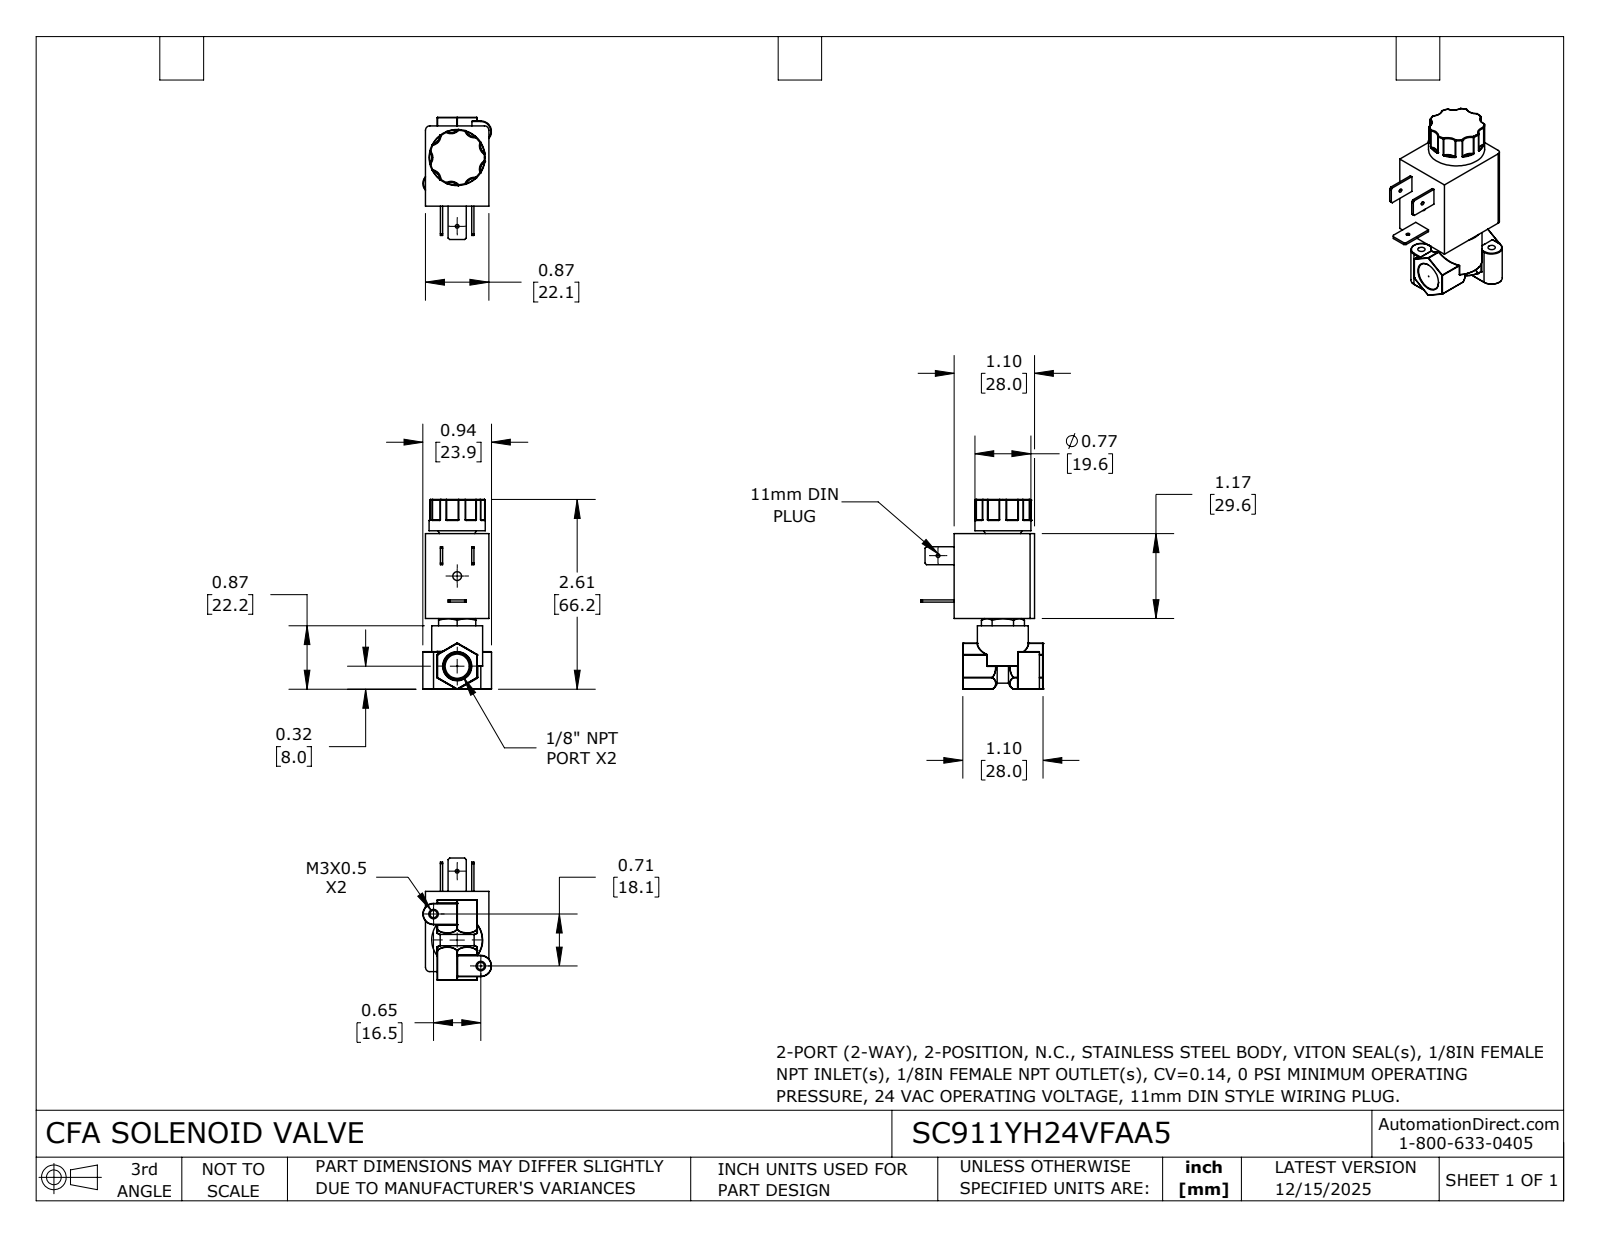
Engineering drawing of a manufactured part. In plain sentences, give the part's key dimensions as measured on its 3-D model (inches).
The part is named "SC911YH24VFAA5". Its 3-D file was written by "SolidWorks 2024 (CONFIG_CONTROL_DESIGN)". It is 1 solid with 393 faces: 76 planar, 108 cylindrical and 209 other. Overall it measures 2.608 by 1.678 by 0.942 inches. Its volume is 1.713 cubic inches and its surface area 14.37 square inches. Round holes: 2 of diameter 0.05, 2 of diameter 0.1, 1 of diameter 0.12. Round bosses or shafts: 1 of diameter 0.77, 1 of diameter 0.7, 1 of diameter 0.332. Partial cylindrical surfaces (rounded edges, fillets, slot ends): 27 of radius 0.004, 18 of radius 0.01, 12 of radius 0.008, 7 of radius 0.133, 2 of radius 0.017, 2 of radius 0.06, 2 of radius 0.132, 2 of radius 0.146. The main face-to-face distances are 0.87, 1.104, 1.167, 1.637, 0.47, 0.548, 0.161, 0.709, 1.207, 0.04. The hole center spacings are 0.672, 0.965, 1.342.
